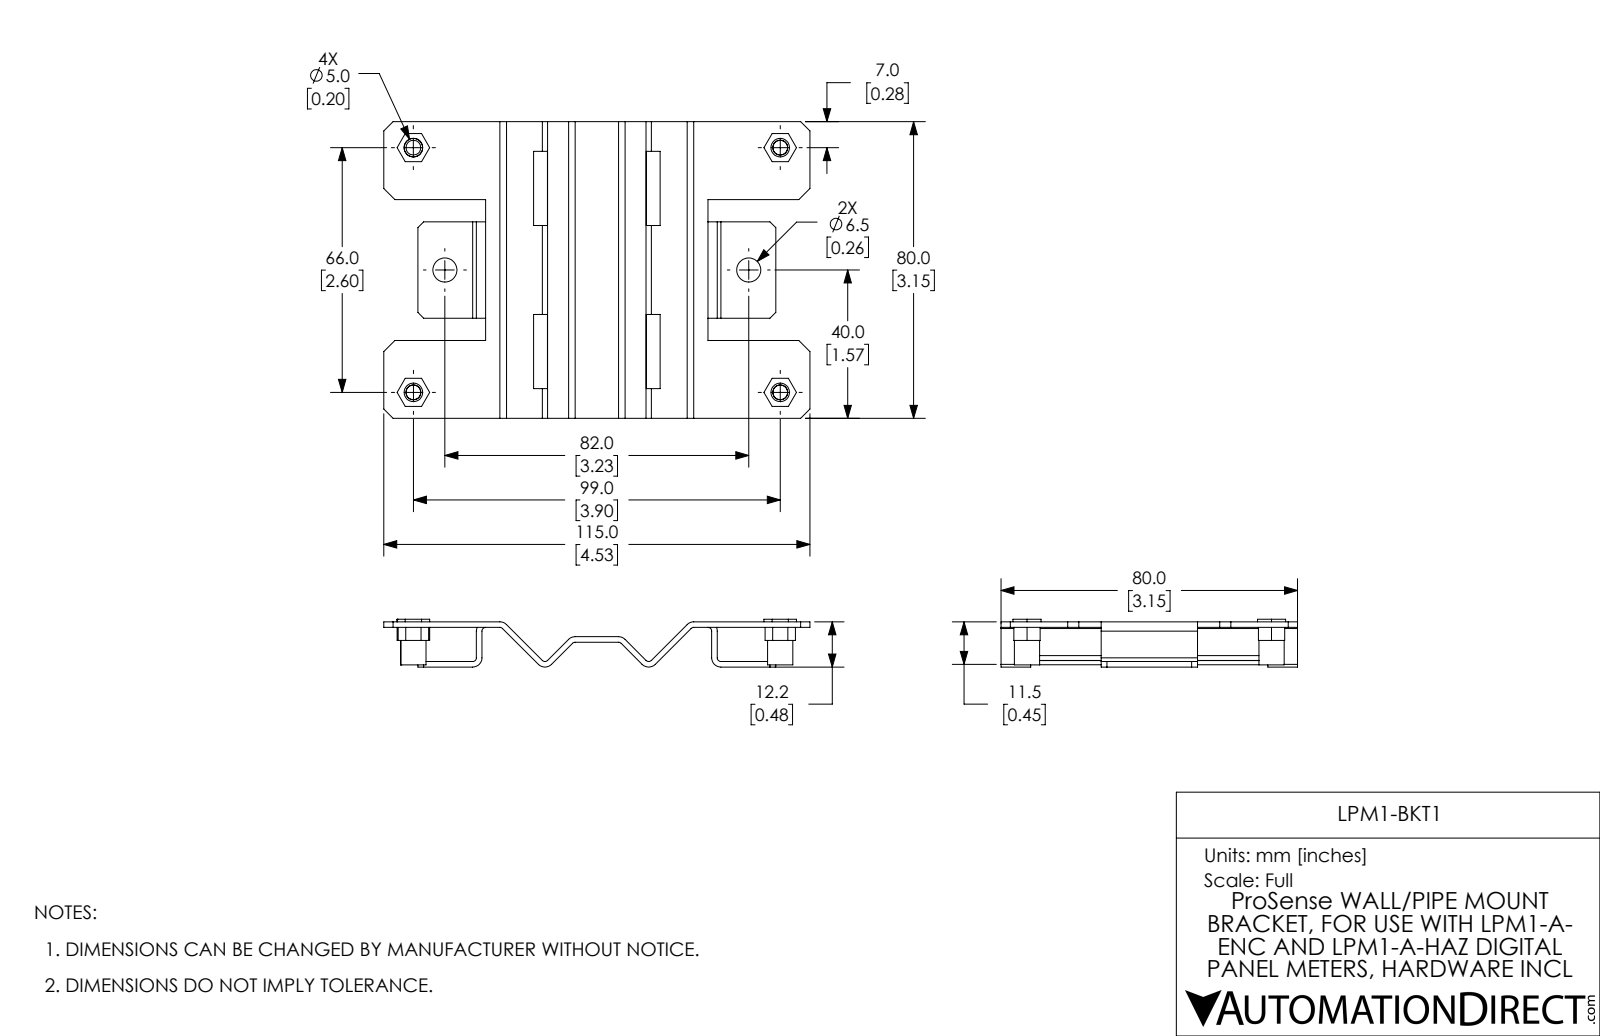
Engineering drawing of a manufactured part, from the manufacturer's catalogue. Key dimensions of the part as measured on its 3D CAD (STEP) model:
Part name (STEP PRODUCT): mountingplate_cpl_0046_asm r1 w EXT1
STEP written by: SolidWorks 2017 (AUTOMOTIVE_DESIGN)
Units: inches
Bodies: 9 solids, 215 faces (167 planar, 48 cylindrical, 0 other)
Overall size (bounding box): 4.528 × 3.15 × 0.508
Volume: 0.952 in³ · Surface area: 34.47 in²
Round holes (diameter × count): ⌀0.157 ×3, ⌀0.256 ×2, ⌀0.197 ×1
Round bosses / shafts (diameter × count): ⌀0.268 ×4, ⌀0.197 ×3
Partial cylindrical surfaces — rounded edges, fillets, slot ends (radius × count): R0.039 ×10, R0.098 ×10
Main face-to-face distances: 0.059, 0.78, 0.157, 0.264, 0.421, 0.72, 0.839, 0.098, 0.217, 0.323
Hole centre spacings: 1.342, 3.793, 2.598, 3.898, 4.684, 3.228
